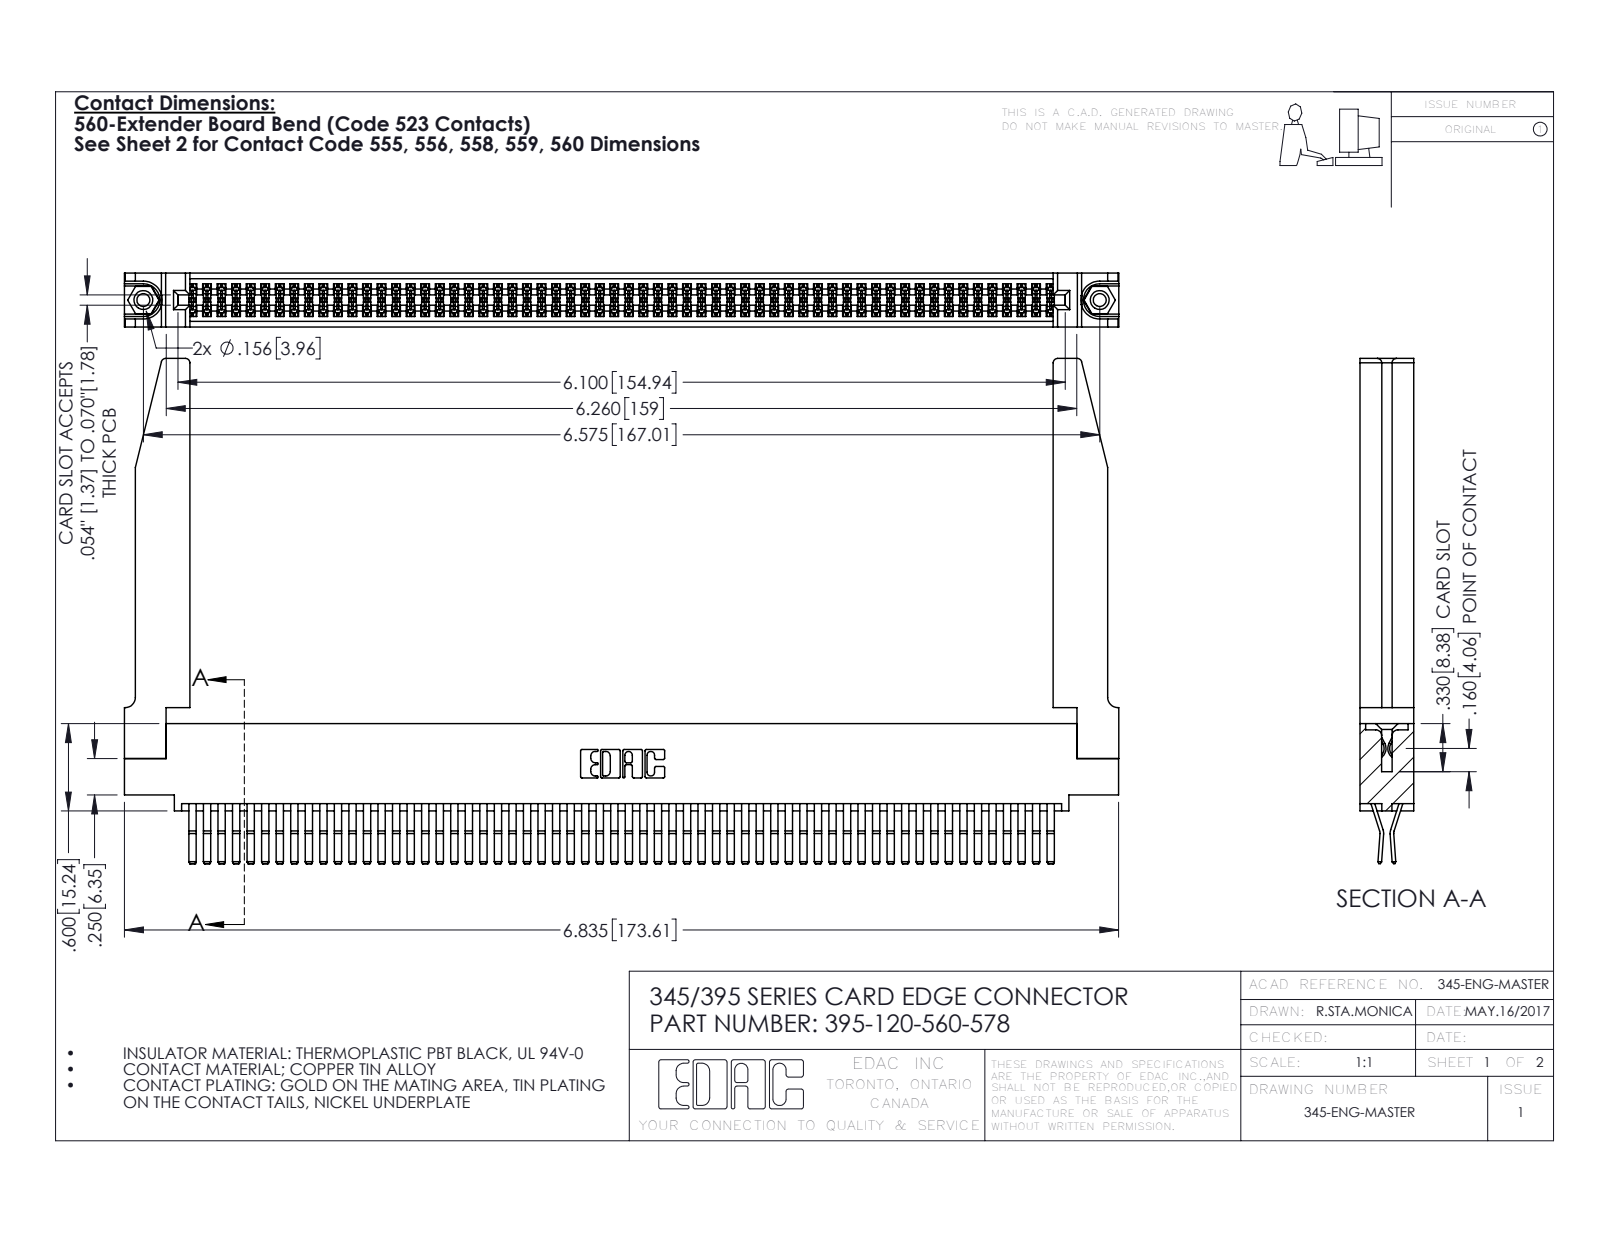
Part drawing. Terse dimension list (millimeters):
name: 345-250-001_345-250-001-102; 345 Part_0.110 Offset - 0.156 Dia-TH; 395-120-560-578; 345-292-001_560 Tail (+1 more)
written by: SolidWorks 2016 (CONFIG_CONTROL_DESIGN)
unit: mm
bodies: 125 solids, 6604 faces (4186 planar, 2366 cylindrical, 52 other)
size: 173.6 × 88.2 × 9.4
volume: 25 510 mm³; area: 35 540 mm²
holes: 2× ⌀2.3, 2× ⌀3.2, 2× ⌀4, 1× ⌀1.6
bosses: 2× ⌀3.9
rounds: 181× R0.2, 22× R0.3, 8× R0.8, 6× R0.2, 6× R0.8, 3× R0.7, 2× R0.3, 2× R0.4
face distances: 1.8, 7.6, 9.4, 0.6, 2.5, 6.9, 5.1, 5.7, 4.4, 3.8
hole spacings: 6.9, 161, 167
